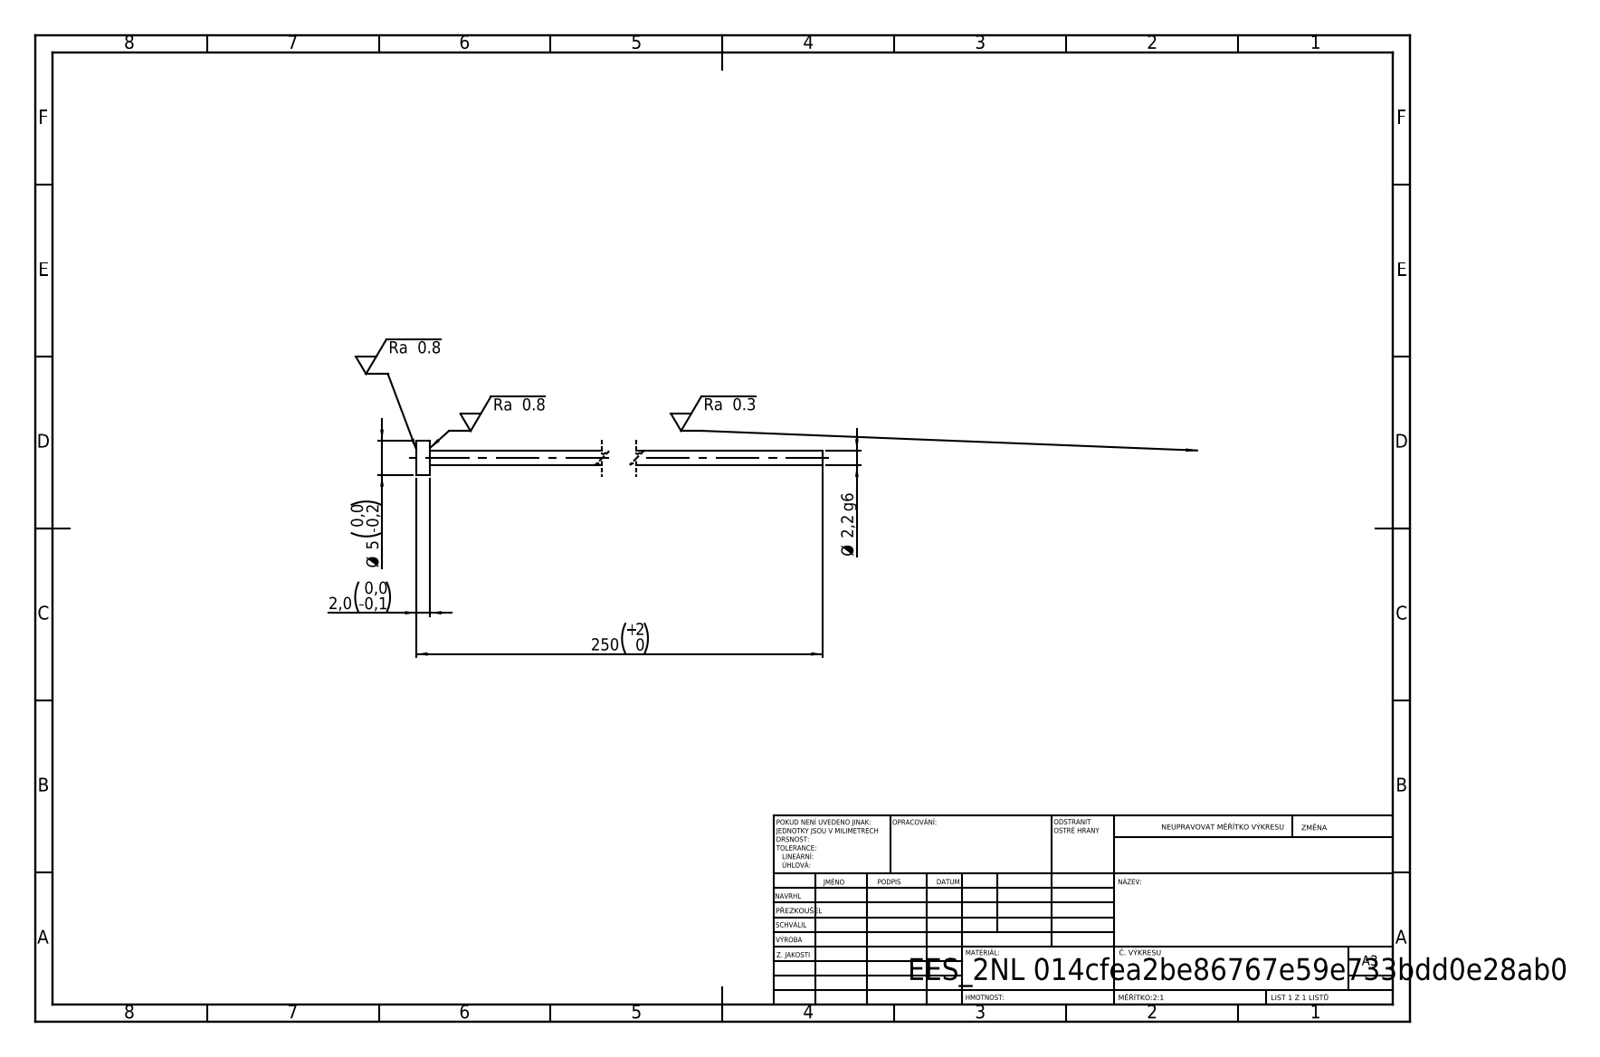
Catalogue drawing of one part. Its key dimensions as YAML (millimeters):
step_written_by: "SolidWorks 2019 (CONFIG_CONTROL_DESIGN)"
units: millimeters
bodies: {solids: 1, faces: 7, planar: 3, cylindrical: 4, other: 0}
overall_size: [250, 5, 5]
volume: 982
surface_area: 1785
round_bosses_or_shafts:
  - {diameter: 5, count: 1}
  - {diameter: 2.2, count: 1}
face_to_face_distances: [2, 250, 248]
